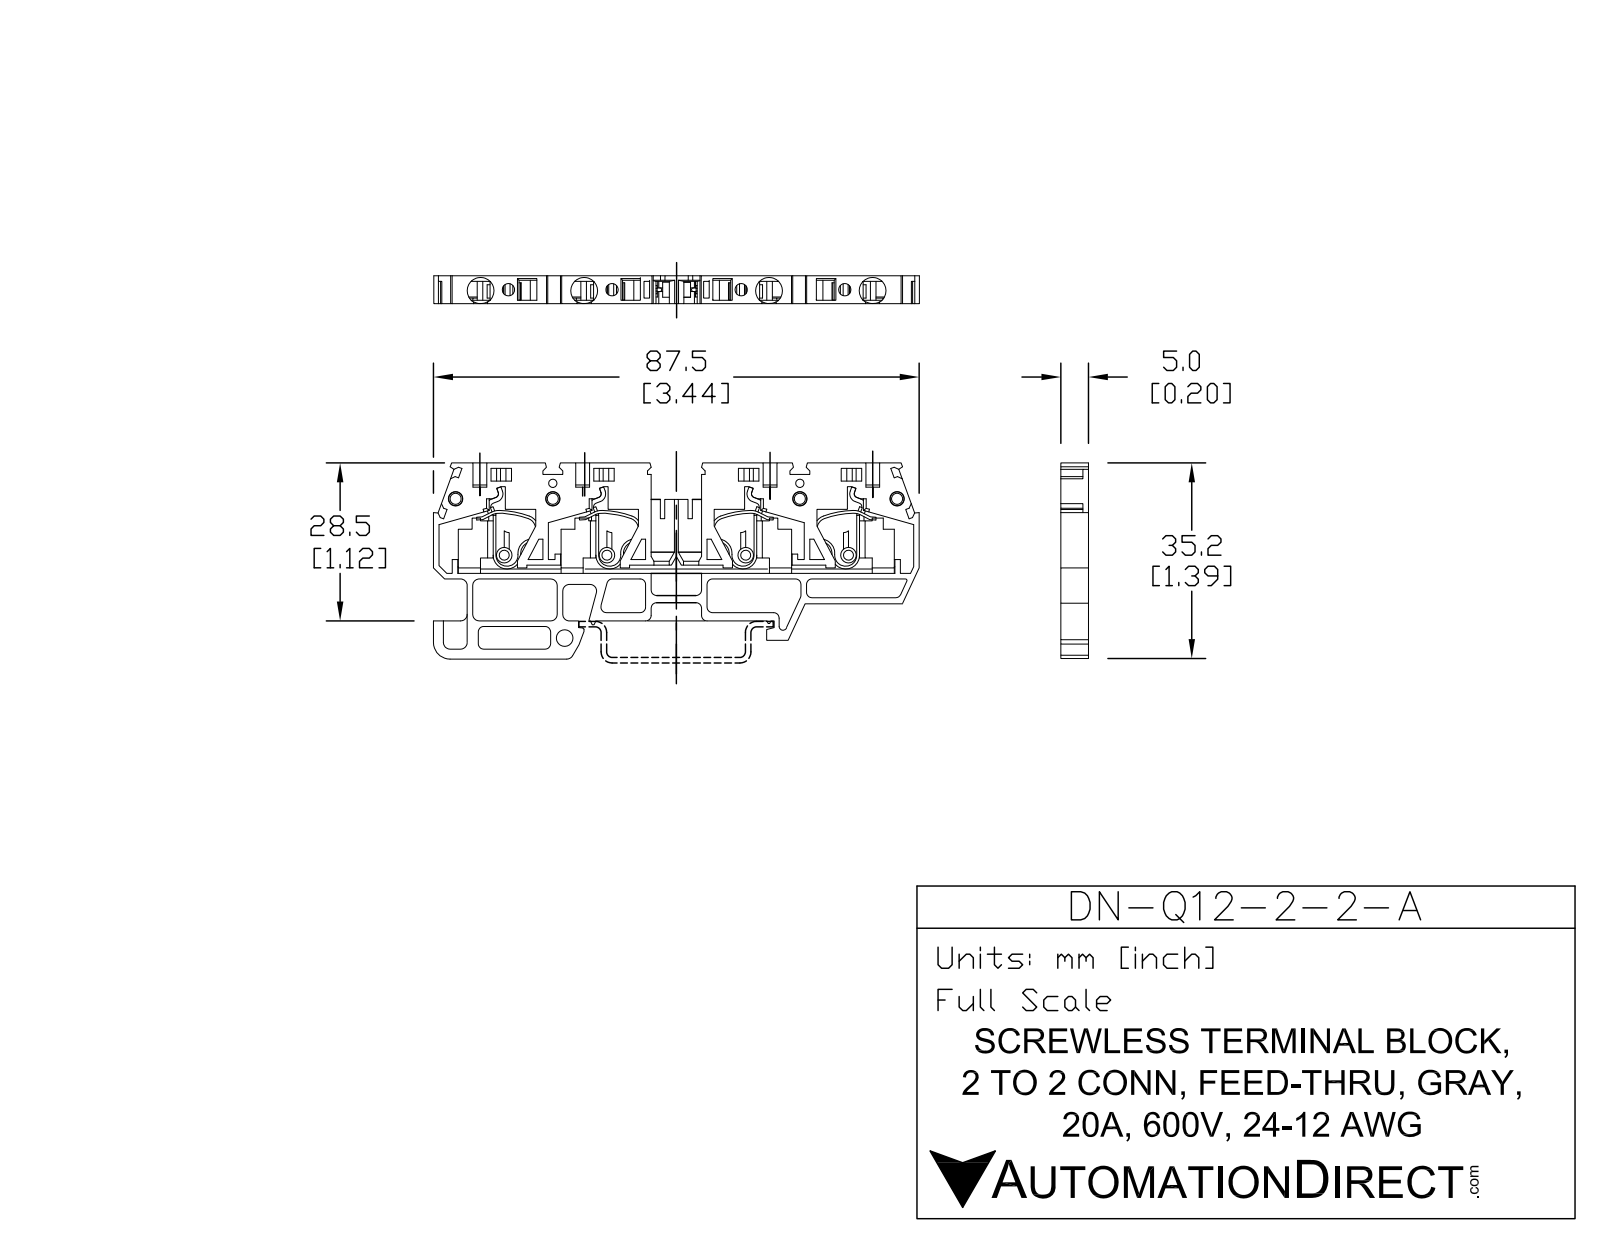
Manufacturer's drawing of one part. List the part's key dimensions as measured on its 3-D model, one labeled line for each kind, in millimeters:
Part name (STEP PRODUCT): 42414_DN-Q12-2-2-A
STEP written by: SolidWorks 2013 (AUTOMOTIVE_DESIGN)
Units: millimetres
Bodies: 1 solid, 460 faces (328 planar, 92 cylindrical, 40 other)
Overall size (bounding box): 87.2 × 35.4 × 5
Volume: 8 282 mm³ · Surface area: 8 692 mm²
Round holes (diameter × count): ⌀2.2 ×4, ⌀2.6 ×4, ⌀4.8 ×4, ⌀1.5 ×2, ⌀3 ×1
Partial cylindrical surfaces — rounded edges, fillets, slot ends (radius × count): R1 ×22, R1.2 ×12, R0.3 ×2, R0.7 ×1, R3 ×1
Main face-to-face distances: 5, 1, 2, 3, 8.4, 4.4, 1.2, 7.5, 0.8, 28.5
Hole centre spacings: 5, 18.6, 46.8, 2.8, 13.6, 17.6, 17.82, 23.6
